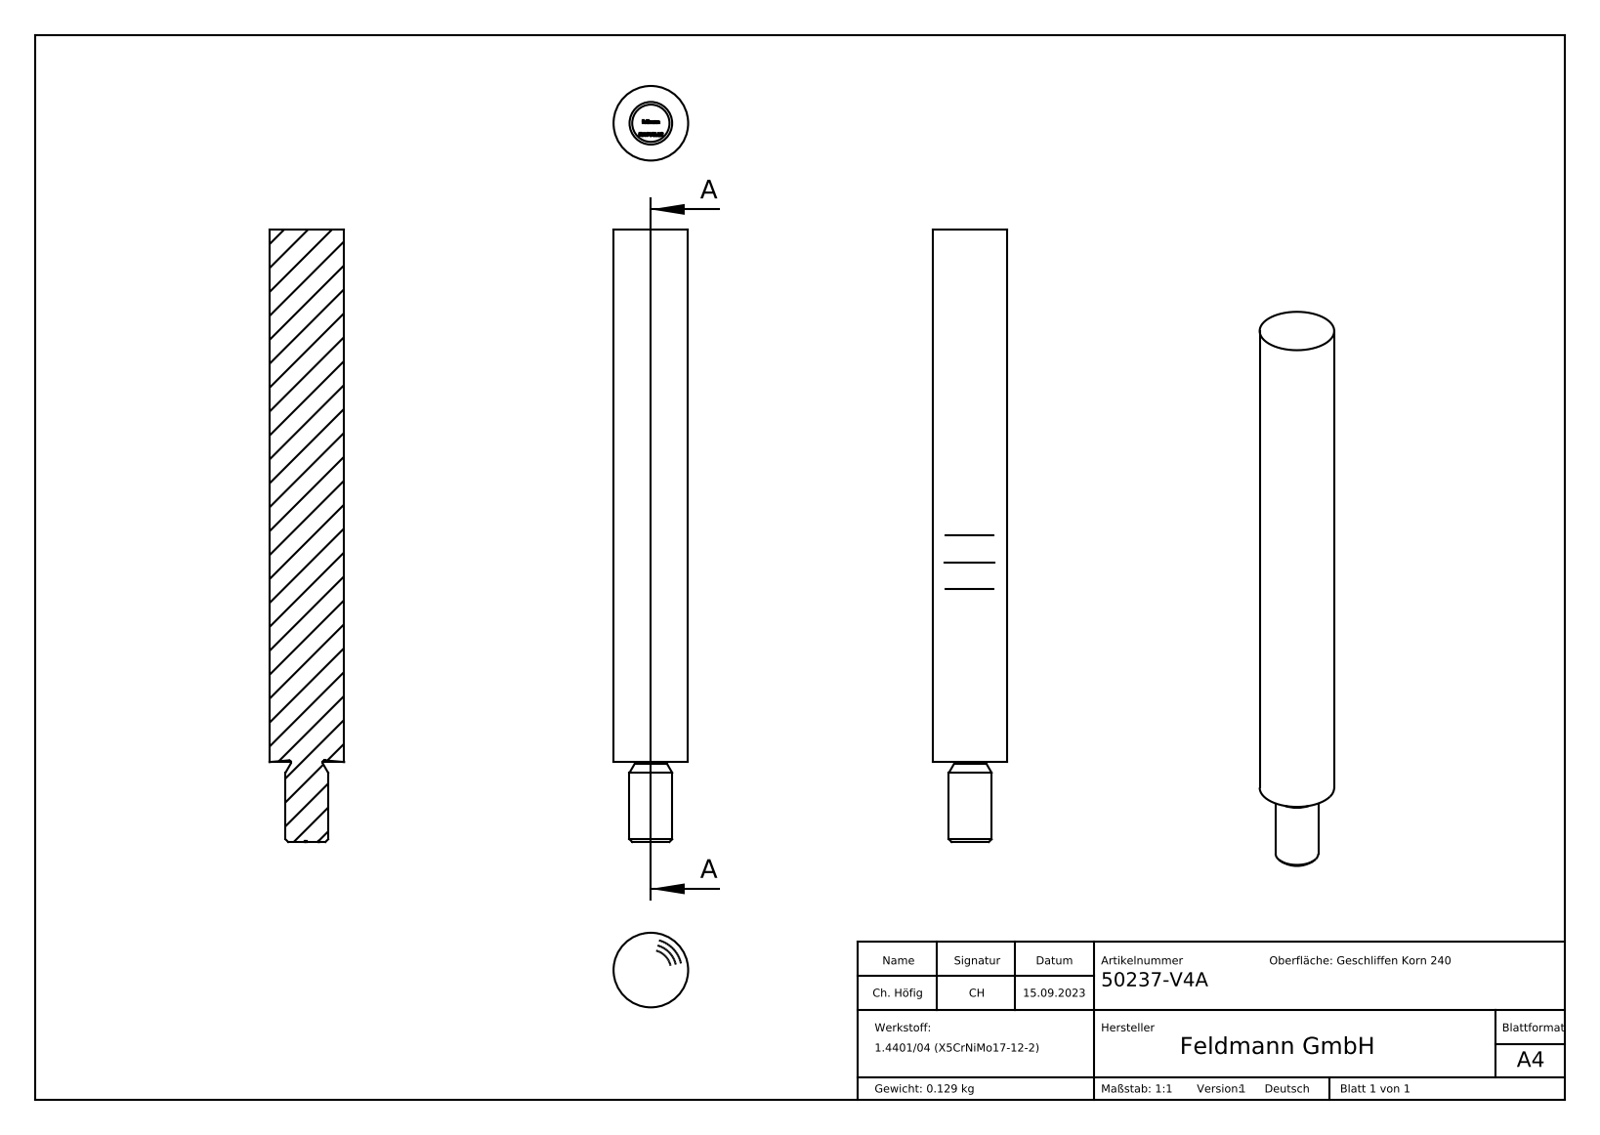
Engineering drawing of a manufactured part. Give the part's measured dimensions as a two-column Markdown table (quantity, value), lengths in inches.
| quantity | value |
| --- | --- |
| part name | 50237-V4A |
| STEP written by | SolidWorks 2018 (CONFIG_CONTROL_DESIGN) |
| units | inches |
| bodies | 1 solid, 266 faces (157 planar, 2 cylindrical, 107 other) |
| overall size | 4.528 × 0.551 × 0.551 |
| volume | 0.982 in³ |
| surface area | 7.913 in² |
| round bosses / shafts (diameter × count) | 0.551 × 1, 0.315 × 1 |
| main face-to-face distances | 4.528, 4.524, 0.03, 0.051, 0.094, 0.094, 0.028, 0.061, 0.096, 0.022 |
